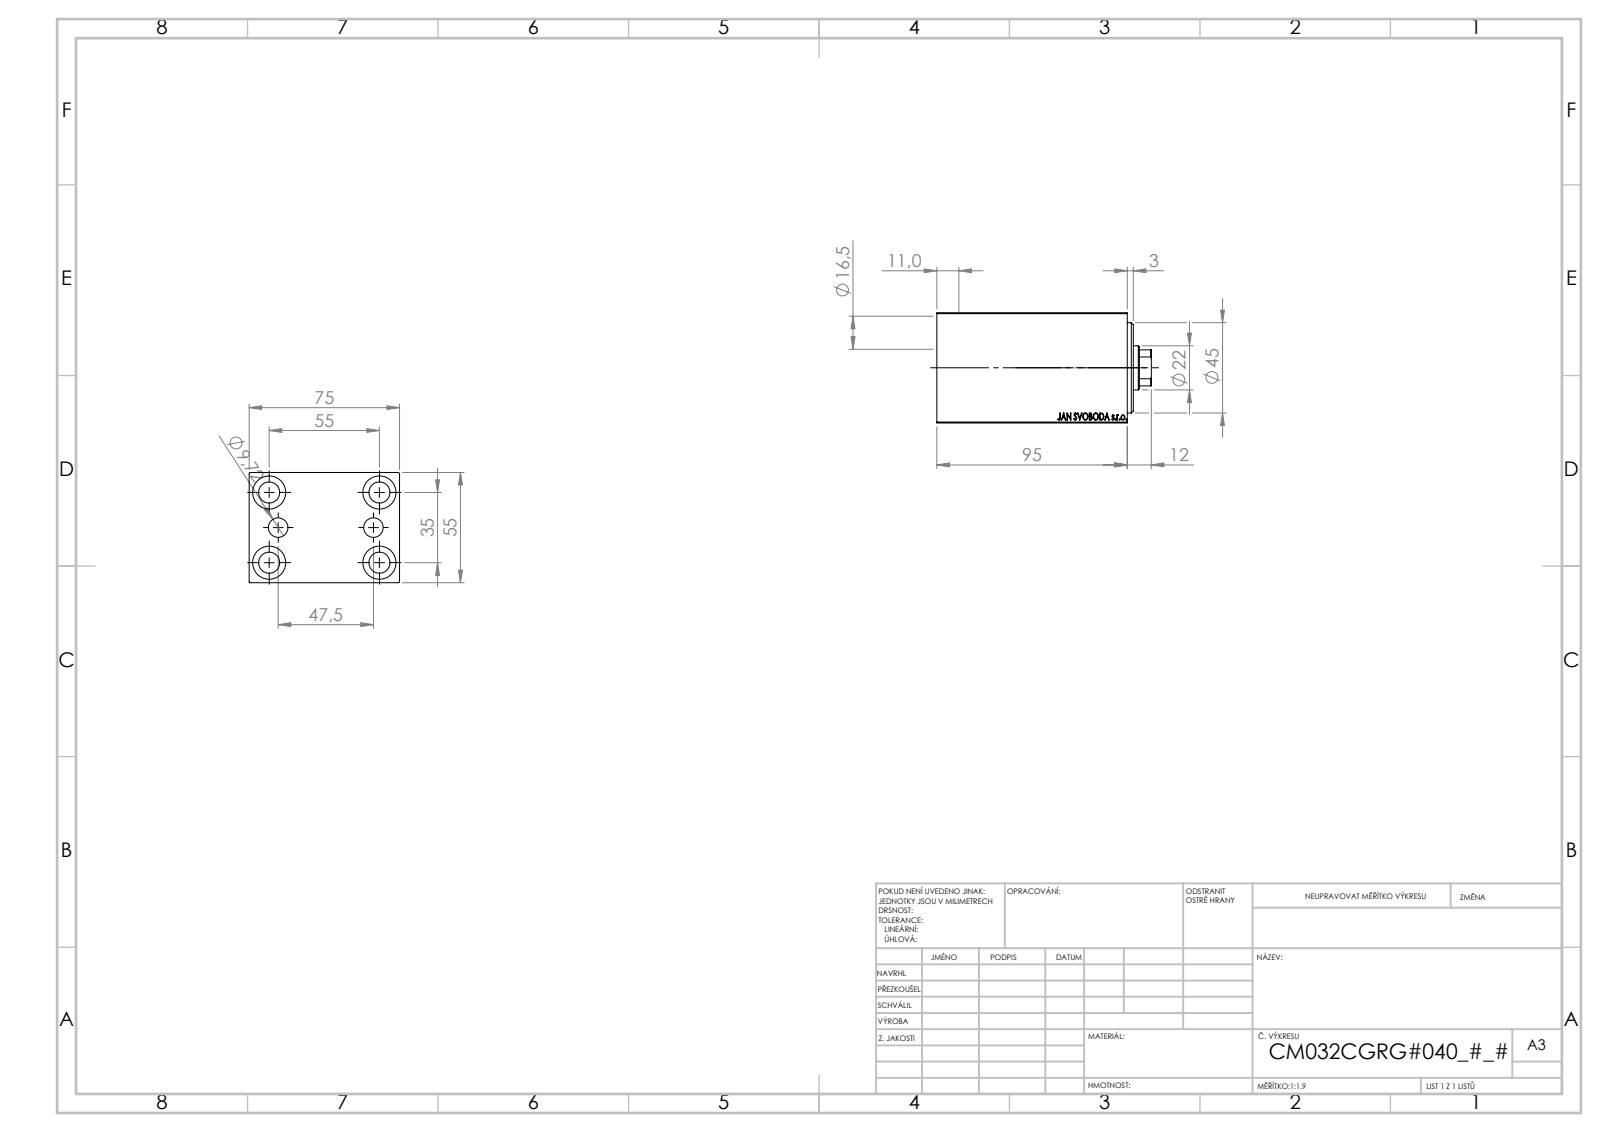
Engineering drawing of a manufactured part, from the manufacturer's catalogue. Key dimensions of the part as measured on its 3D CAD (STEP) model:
Part name (STEP PRODUCT): V450CM_C_VCP; V450CM_VC_B; V450CM_C_Body
STEP written by: SolidWorks 2019 (CONFIG_CONTROL_DESIGN)
Units: millimetres
Bodies: 3 solids, 858 faces (408 planar, 56 cylindrical, 394 other)
Overall size (bounding box): 107 × 75 × 55
Volume: 333 060 mm³ · Surface area: 68 373 mm²
Round holes (diameter × count): ⌀10.5 ×5, ⌀16.5 ×4, ⌀4 ×2, ⌀9.72 ×2, ⌀22 ×1, ⌀25.5 ×1, ⌀32 ×1, ⌀34 ×1, ⌀45 ×1
Partial cylindrical surfaces — rounded edges, fillets, slot ends (radius × count): R10.5 ×1
Main face-to-face distances: 55, 75, 5, 31.25, 63.75, 95, 90, 58.75, 11, 84
Hole centre spacings: 17.9, 32.6, 54.16, 23.75, 35, 55, 65.19, 47.5
